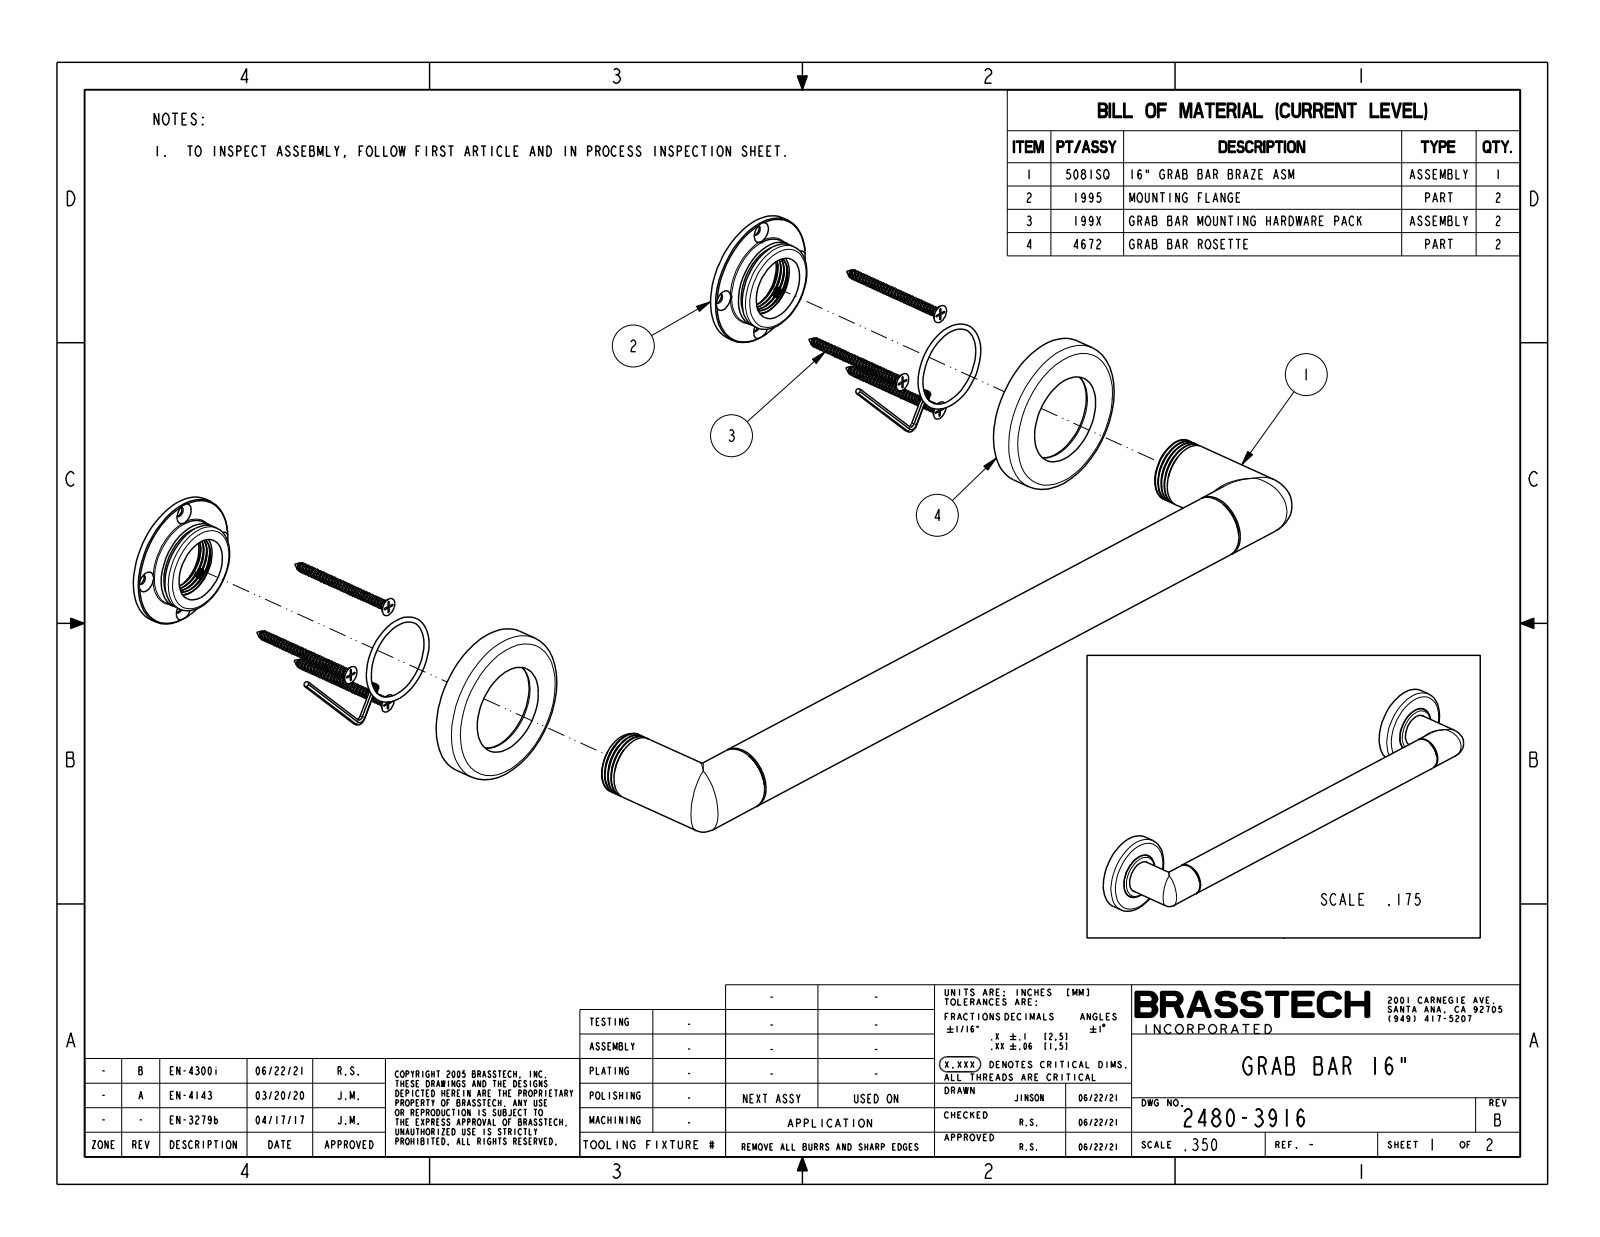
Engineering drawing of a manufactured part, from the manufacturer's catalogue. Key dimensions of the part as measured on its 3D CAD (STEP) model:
Part name (STEP PRODUCT): 2480-3916
STEP written by: CREO PARAMETRIC BY PTC INC, 2018400 (CONFIG_CONTROL_DESIGN)
Units: inches
Bodies: 1 solid, 48 faces (6 planar, 18 cylindrical, 24 other)
Overall size (bounding box): 19 × 3 × 2.755
Volume: 31.1 in³ · Surface area: 109.9 in²
Round bosses / shafts (diameter × count): ⌀1.25 ×3, ⌀3 ×2, ⌀1.75 ×2
Main face-to-face distances: 0.53, 0.6, 0.07
